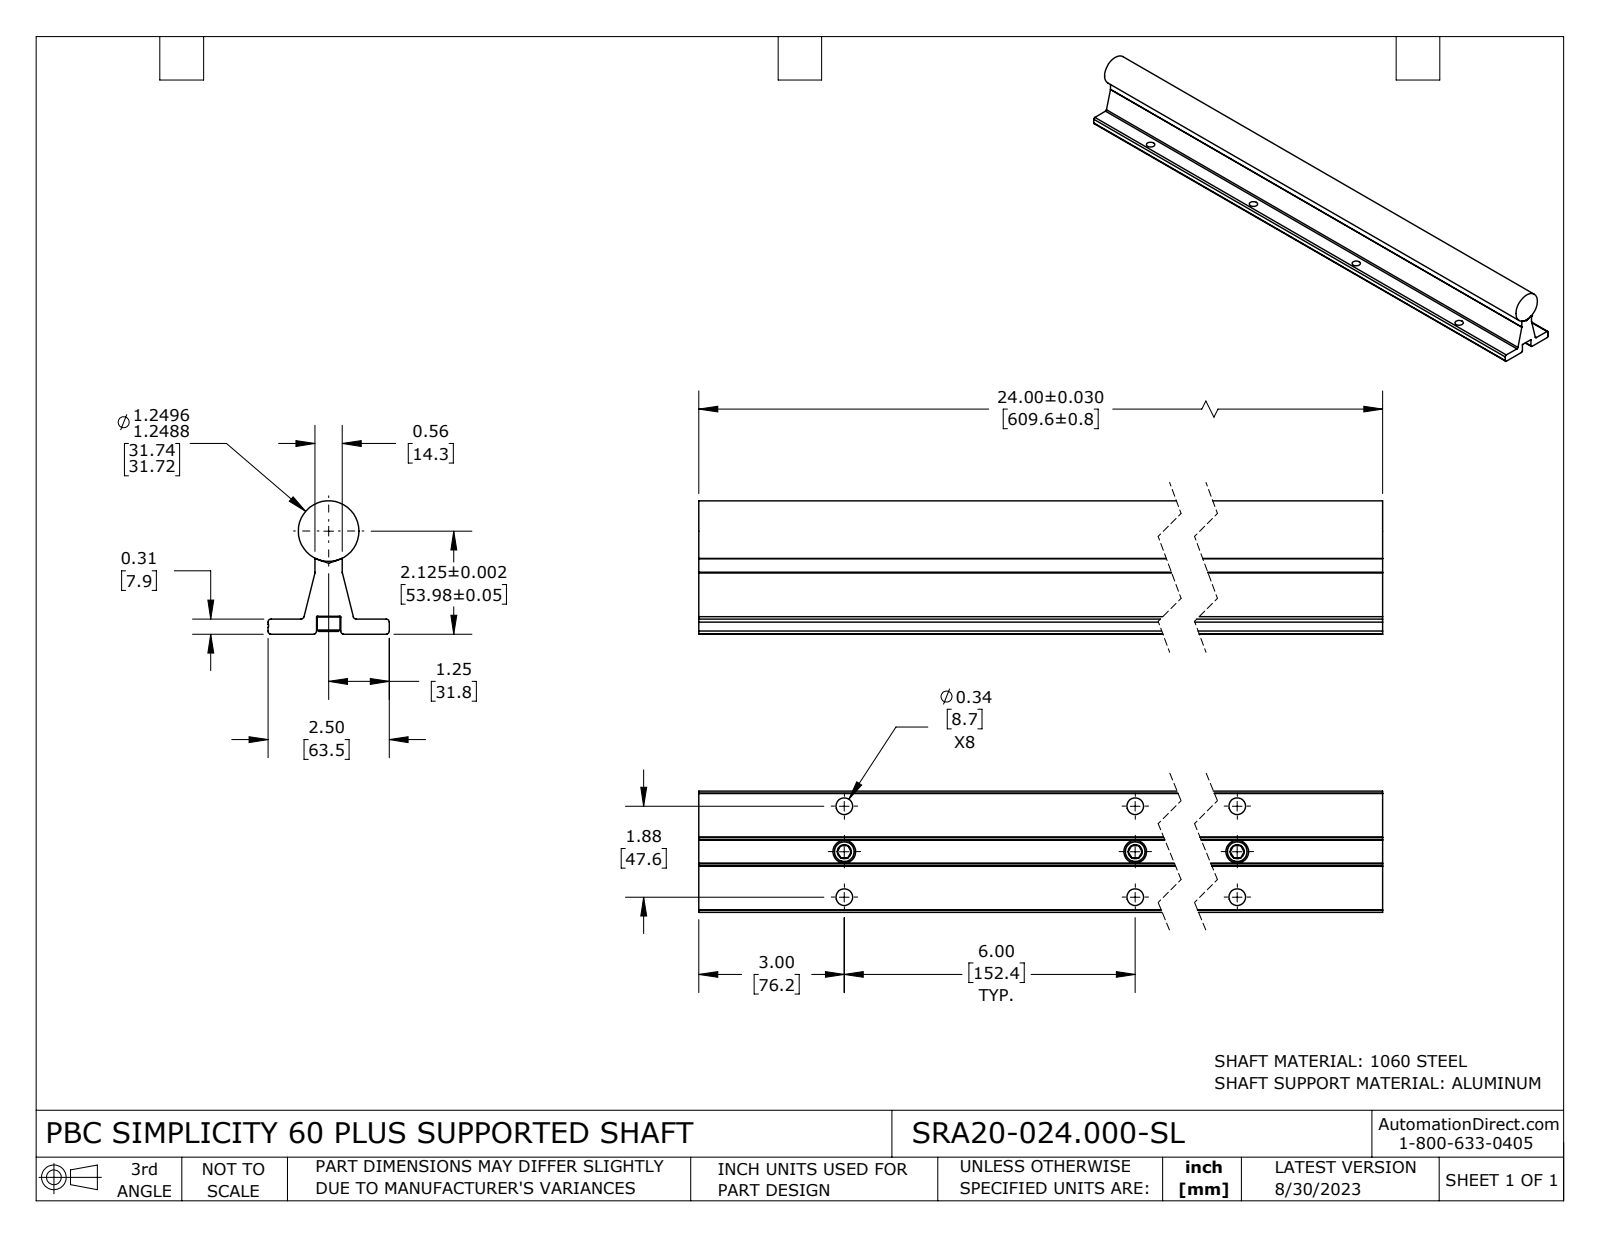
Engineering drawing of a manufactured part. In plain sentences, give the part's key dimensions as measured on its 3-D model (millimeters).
The part is named "SRA20-024.000-SL". Its 3-D file was written by "SolidWorks 2021 (CONFIG_CONTROL_DESIGN)". It is 6 solids with 203 faces: 71 planar, 72 cylindrical and 60 other. Overall it measures 609.6 by 69.9 by 63.5 millimeters. Its volume is 1 068 000 cubic millimeters and its surface area 204 900 square millimeters. Round holes: 12 of diameter 8.7, 4 of diameter 6.9, 4 of diameter 9.5. Round bosses or shafts: 4 of diameter 11.9, 4 of diameter 8, 1 of diameter 31.8. Partial cylindrical surfaces (rounded edges, fillets, slot ends): 6 of radius 1.6, 3 of radius 1.6, 2 of radius 0.4, 2 of radius 0.8, 1 of radius 1.6. The main face-to-face distances are 8, 0.8, 13.5, 9.3, 1.4, 24.6, 25.4, 38.1, 38.9, 12.7. The hole center spacings are 154.3, 152.4, 23.8, 305.7, 159.7, 304.8, 47.6, 308.5.
